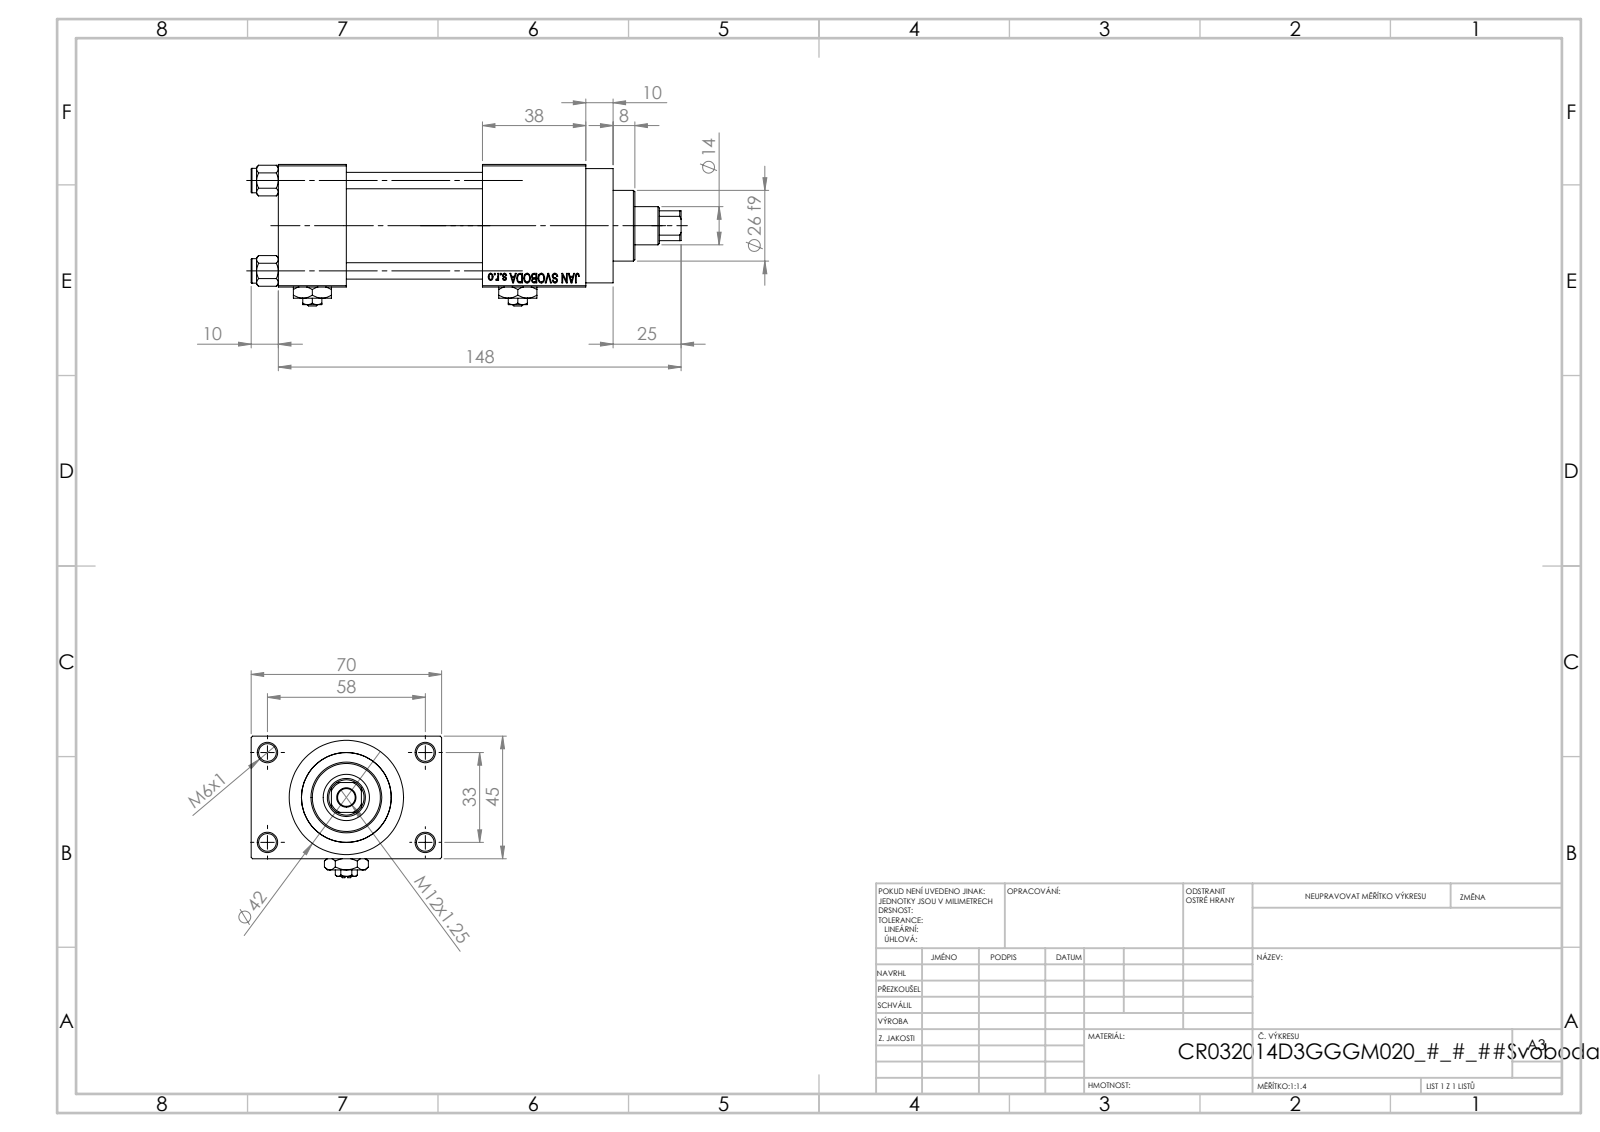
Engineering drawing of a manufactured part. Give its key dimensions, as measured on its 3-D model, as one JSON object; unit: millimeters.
{"part_name": "V215CR_D_Body; NUT_M5_D; Zatka_pro_OIL_PORT; V215_VC_A (+2 more)", "step_written_by": "SolidWorks 2019 (CONFIG_CONTROL_DESIGN)", "units": "millimeters", "bodies": {"solids": 13, "faces": 1202, "planar": 542, "cylindrical": 100, "other": 560}, "overall_size": [158, 70, 52], "volume_mm3": 230698, "surface_area_mm2": 76617, "round_holes": [[6.5, 5], [6, 4], [7, 2], [13.16, 2], [20, 2], [14, 1], [17, 1], [24, 1], [32, 1], [33, 1]], "round_bosses_or_shafts": [[9, 4], [42, 1], [38, 1], [26, 1]], "partial_cylinders_radius": [[6.5, 1]], "face_to_face_distances": [45, 25, 12.5, 57.5, 50, 75, 88, 70, 38, 113], "hole_center_spacings": [12.4, 23.48, 33.2, 33.37, 35.35, 45.6, 56.35, 33]}
